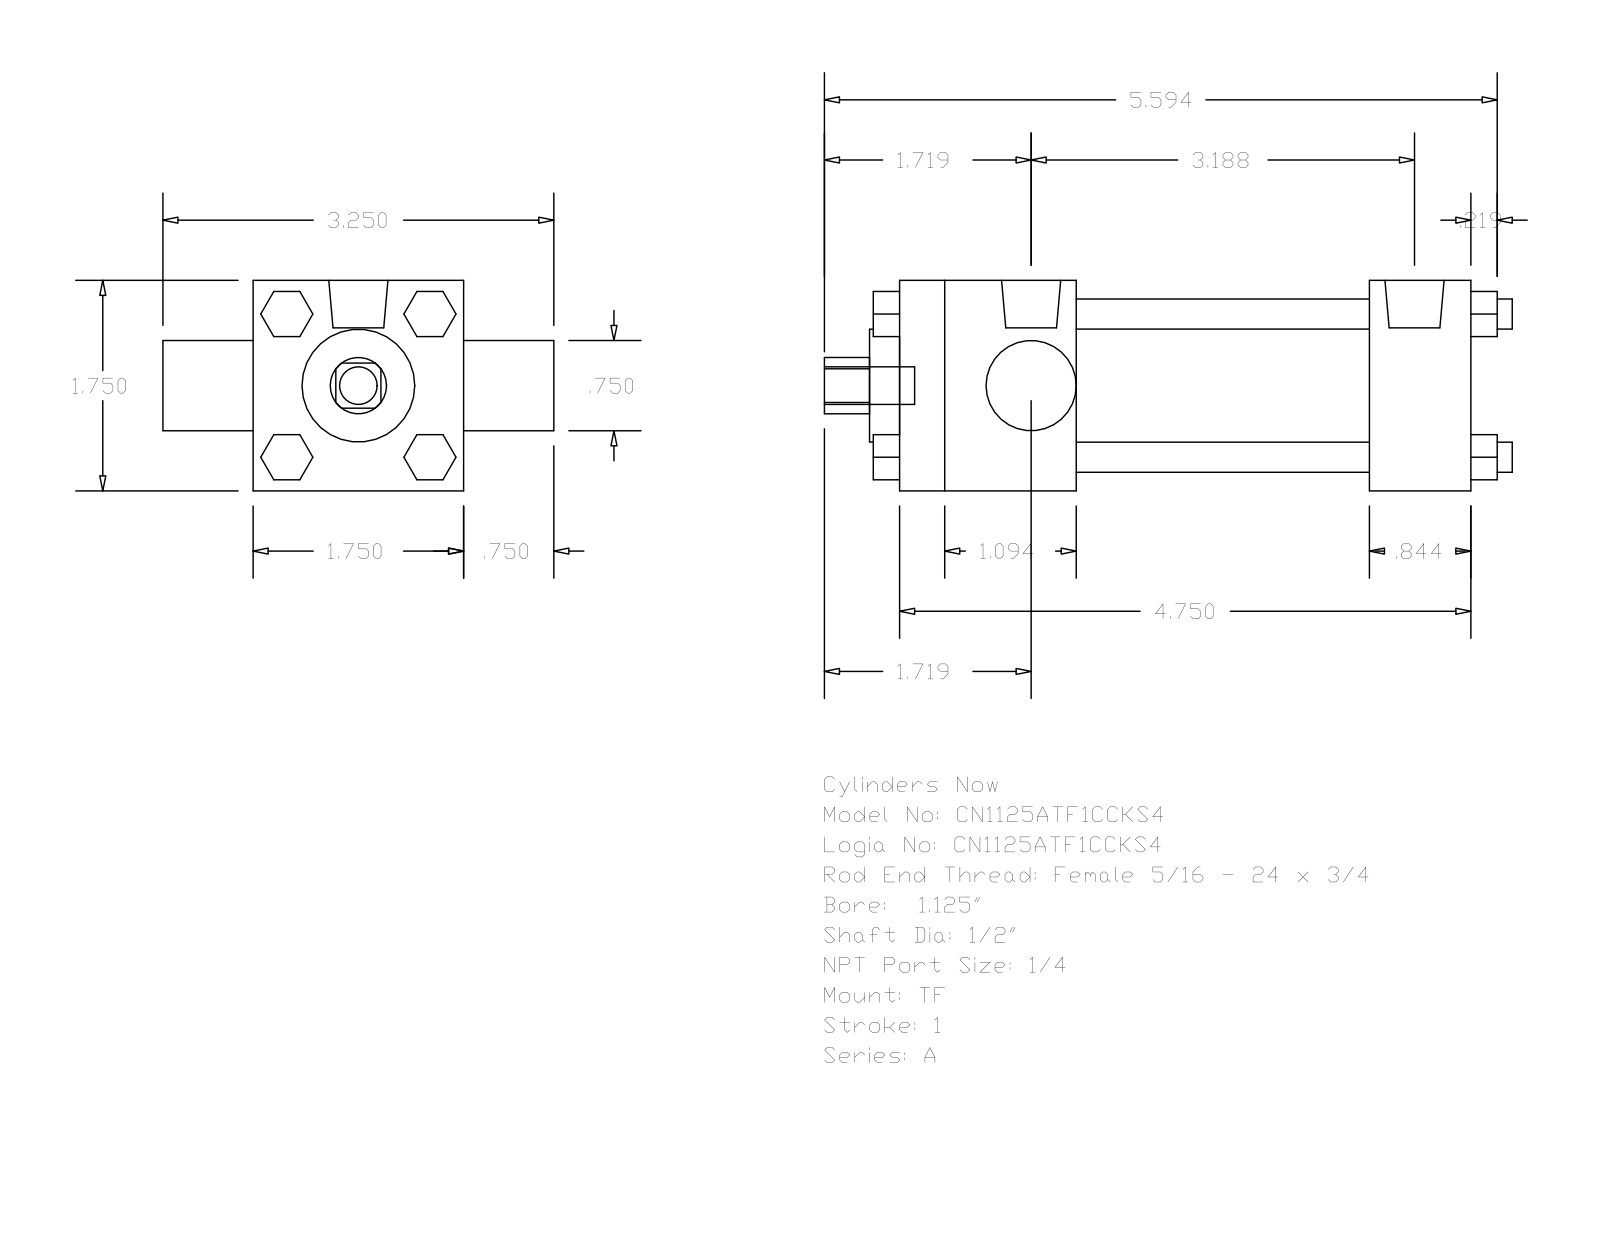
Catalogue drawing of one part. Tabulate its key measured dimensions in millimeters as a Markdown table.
| quantity | value |
| --- | --- |
| part name | A_TF__0112_0.5 |
| STEP written by | GSSL Pune (CONFIG_CONTROL_DESIGN) |
| units | millimeters |
| bodies | 0 solids, 120 faces (92 planar, 28 cylindrical, 0 other) |
| overall size | 145.26 × 82.55 × 44.45 |
| round holes (diameter × count) | 12.7 × 1, 19.05 × 1, 23.81 × 1, 31.88 × 1 |
| round bosses / shafts (diameter × count) | 6.35 × 4, 5.56 × 3, 12.49 × 2, 7.94 × 1 |
| partial cylindrical surfaces (radius × count) | 5.94 × 1 |
| main face-to-face distances | 44.46, 120.65, 99.21, 21.44, 37.3, 61.91, 83.35, 19.04, 63.5, 9.53 |
